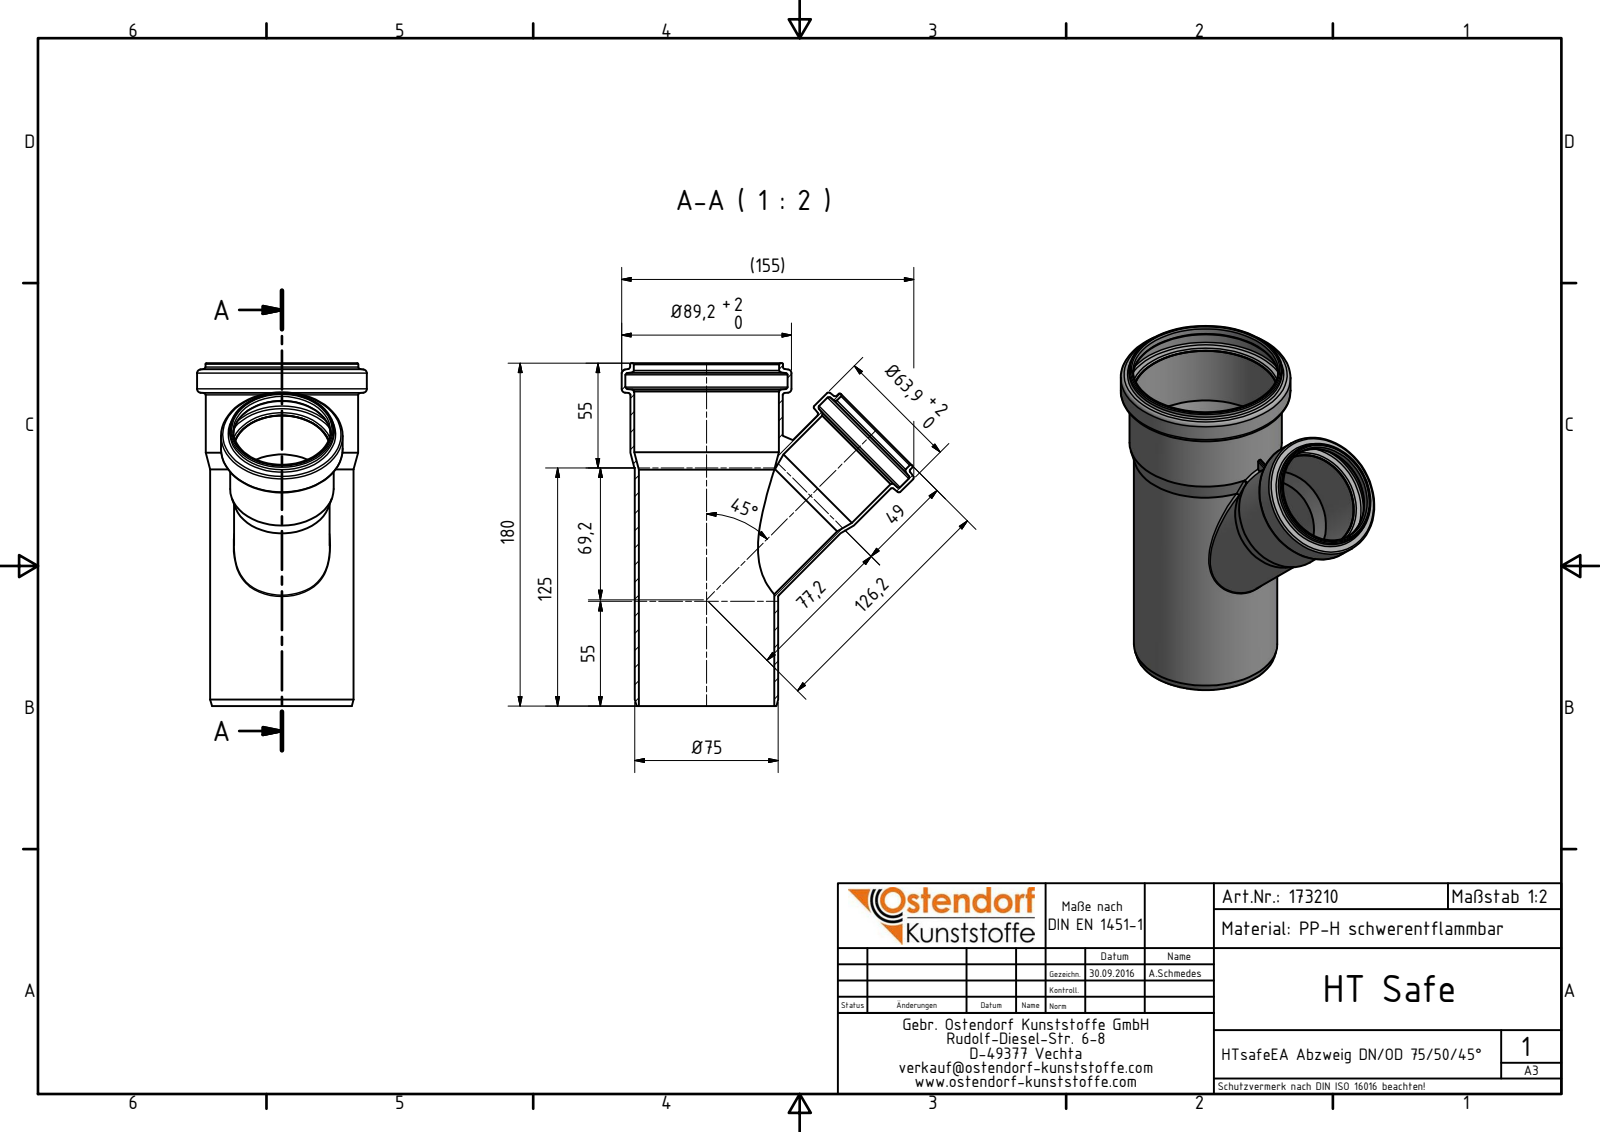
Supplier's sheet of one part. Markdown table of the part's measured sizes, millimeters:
| quantity | value |
| --- | --- |
| part name | 173210 HTsafeEA DN_OD 75_50_45° |
| STEP written by | Autodesk Inventor 2016 (AUTOMOTIVE_DESIGN) |
| units | millimeters |
| bodies | 1 solid, 68 faces (8 planar, 20 cylindrical, 40 other) |
| overall size | 180 × 153.49 × 89.2 |
| volume | 112 999 mm³ |
| surface area | 112 475 mm² |
| round holes (diameter × count) | 46.2 × 1, 50.8 × 1, 51.1 × 1, 60.3 × 1, 71.1 × 1, 76 × 1, 76.3 × 1, 85.2 × 1 |
| round bosses / shafts (diameter × count) | 89.2 × 1, 80.3 × 1, 80 × 1, 75.3 × 1, 63.9 × 1, 54.7 × 1, 54.4 × 1, 50.2 × 1 |
| partial cylindrical surfaces (radius × count) | 0.5 × 2 |
| main face-to-face distances | 180, 165.11, 14.89, 14.9, 2 |
